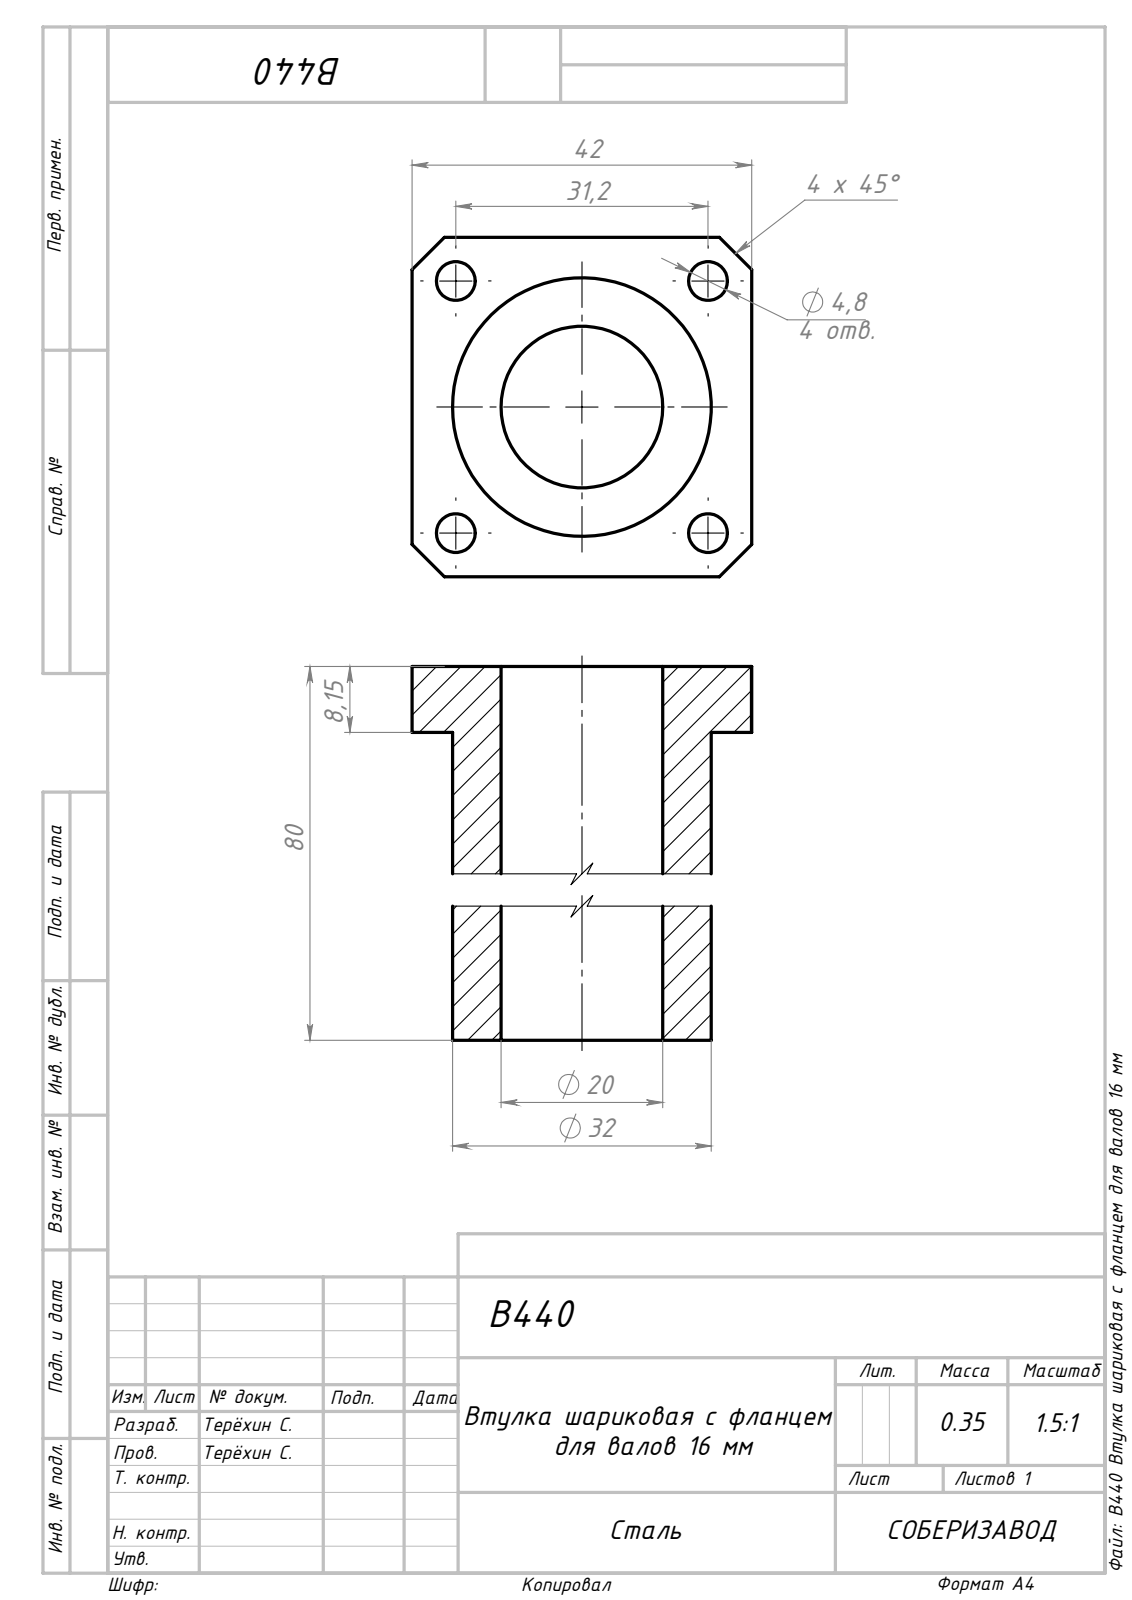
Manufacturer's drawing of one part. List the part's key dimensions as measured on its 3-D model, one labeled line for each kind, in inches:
Part name (STEP PRODUCT): Сборка3; B440 Втулка шариковая с фланцем для валов 16 мм_00
STEP written by: SolidWorks 2024 (AUTOMOTIVE_DESIGN)
Units: inches
Bodies: 1 solid, 43 faces (15 planar, 20 cylindrical, 8 other)
Overall size (bounding box): 3.15 × 1.654 × 1.654
Volume: 2.768 in³ · Surface area: 26.27 in²
Round holes (diameter × count): ⌀0.189 ×4, ⌀0.354 ×4, ⌀0.787 ×1
Round bosses / shafts (diameter × count): ⌀1.26 ×1
Main face-to-face distances: 0.321, 1.654, 3.15, 2.829, 0.177, 0.144, 2.972, 2.116
Hole centre spacings: 0.869, 1.228, 1.737
